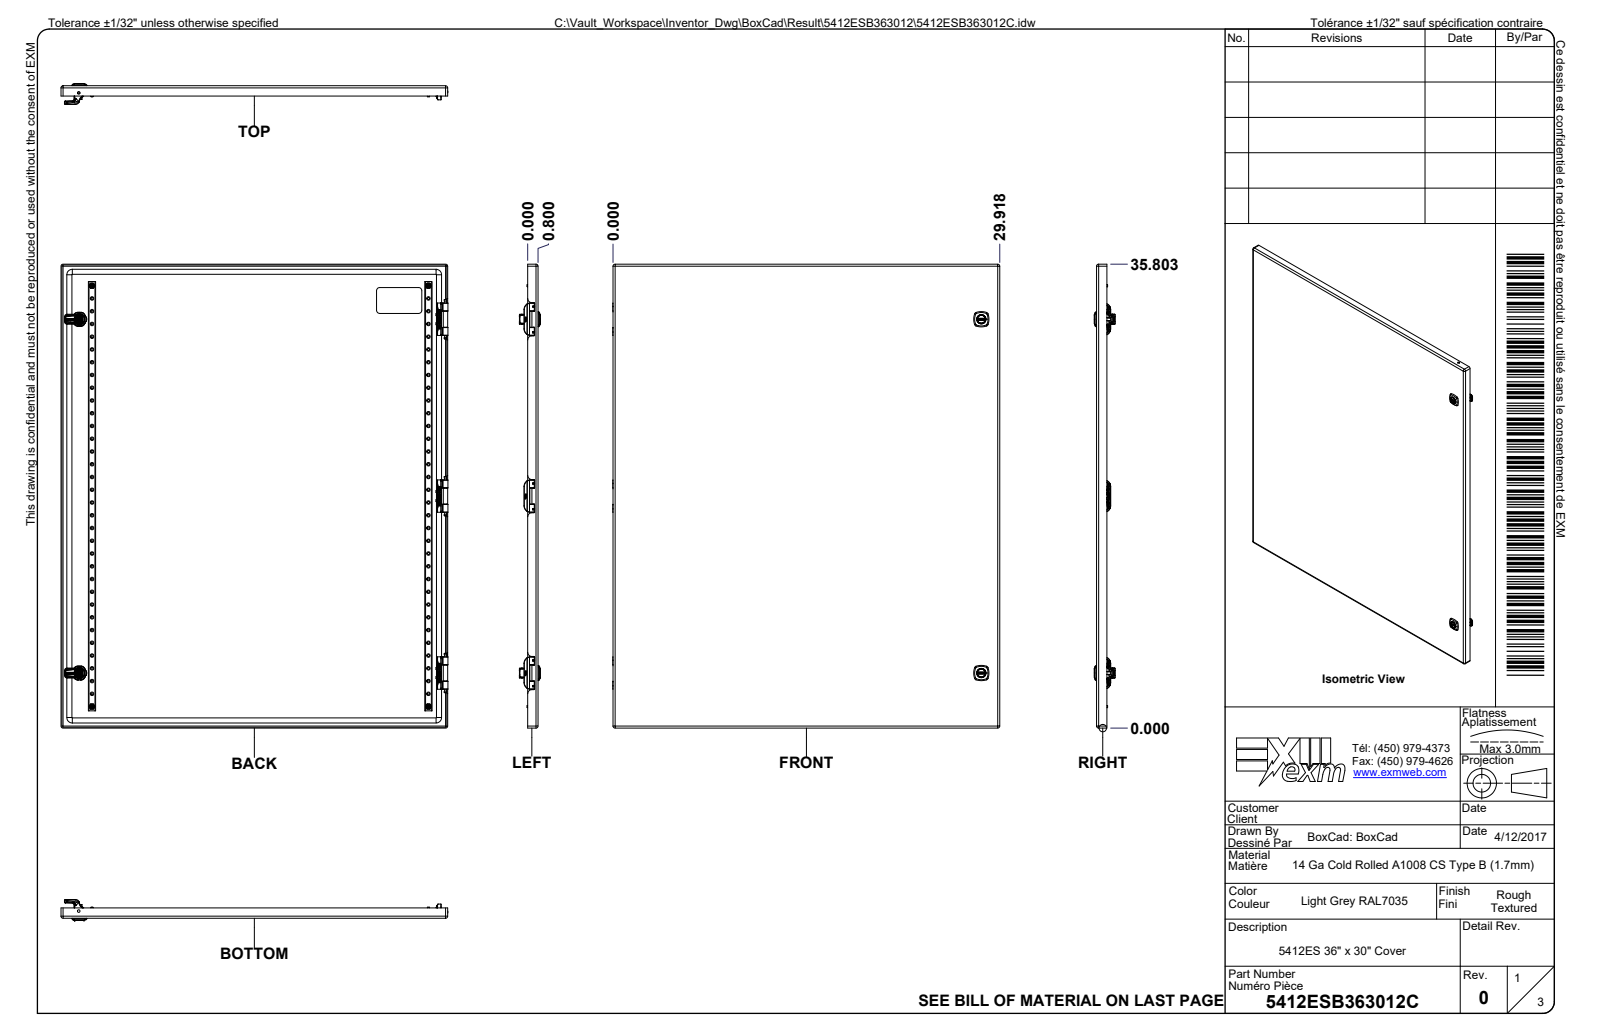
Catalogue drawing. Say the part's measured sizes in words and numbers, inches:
The part is named "5412ESB363012; 5412ESB363012B; 5412ESB363012B-P; STK-Q-16005 (+8 more)". Its 3-D file was written by "Autodesk Inventor 2024 (AUTOMOTIVE_DESIGN)". It is 78 solids with 12702 faces: 3727 planar, 3273 cylindrical and 5702 other. Overall it measures 36 by 30.018 by 13.295 inches. Its volume is 399.6 cubic inches and its surface area 10 621 square inches. Round holes: 64 of diameter 0.165, 12 of diameter 0.043, 11 of diameter 0.03, 10 of diameter 0.315, 9 of diameter 0.201, 6 of diameter 0.178, 6 of diameter 0.27, 6 of diameter 0.311, 4 of diameter 0.197, 4 of diameter 0.268, 4 of diameter 0.29, 4 of diameter 0.39. Round bosses or shafts: 64 of diameter 0.237, 12 of diameter 0.039, 11 of diameter 0.03, 10 of diameter 0.232, 6 of diameter 0.717, 6 of diameter 0.311, 6 of diameter 0.262, 4 of diameter 0.374. Partial cylindrical surfaces (rounded edges, fillets, slot ends): 291 of radius 0.02, 169 of radius 0.01, 143 of radius 0.039, 124 of radius 0.008, 50 of radius 0.012, 44 of radius 0.016, 32 of radius 0.031, 26 of radius 0.004. The main face-to-face distances are 0.068, 13.052, 12.983, 13.12, 0.942, 0.874, 12.109, 12.178, 1.047, 0.979. The hole center spacings are 1.969, 13.652, 0.984, 2.953, 3.937, 27.303, 0.35, 0.735.
